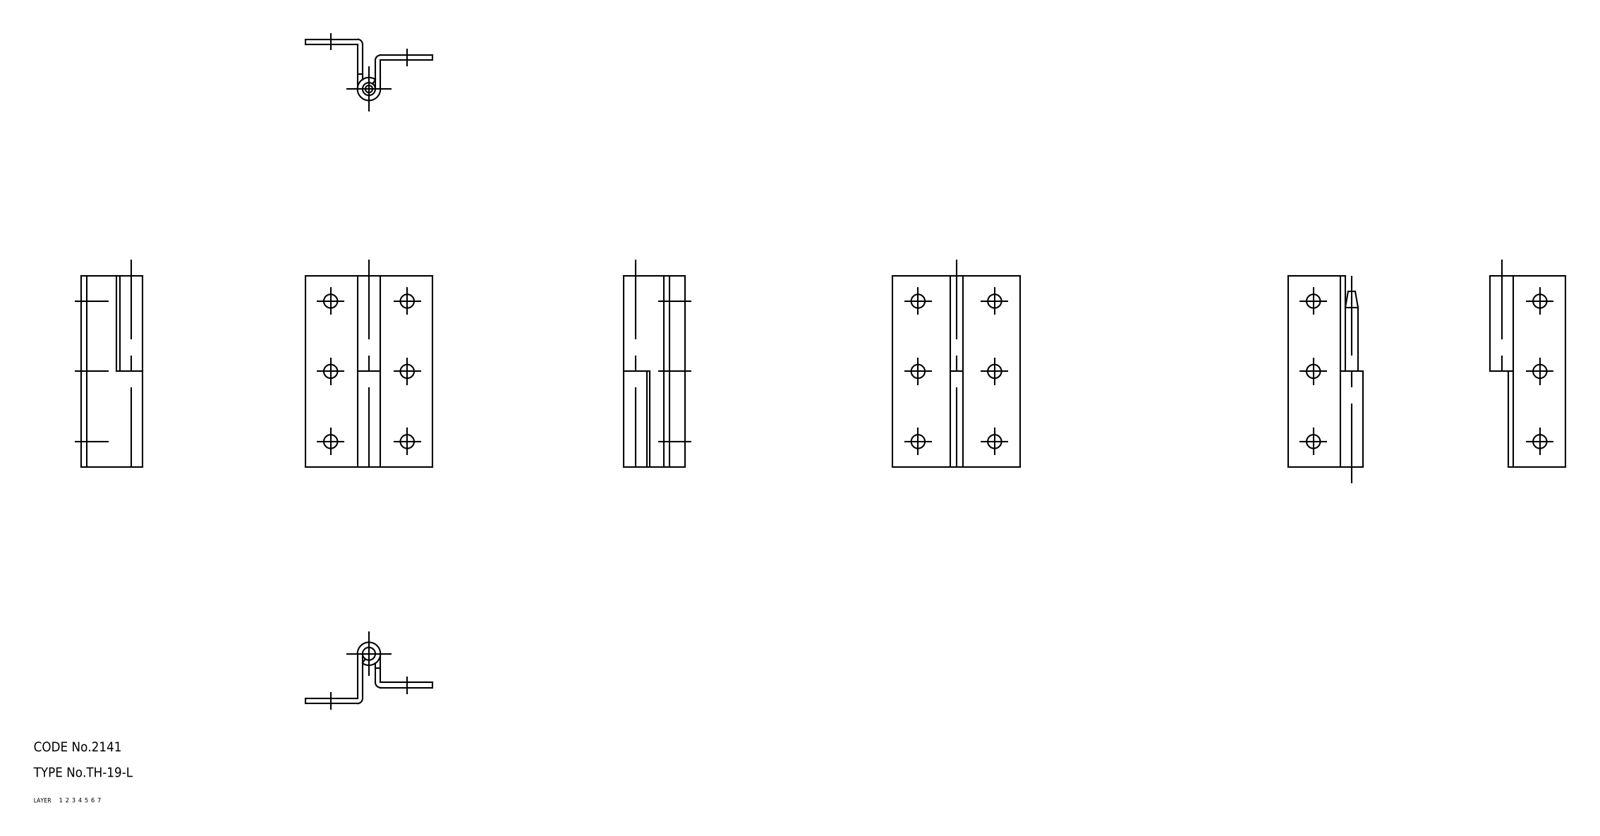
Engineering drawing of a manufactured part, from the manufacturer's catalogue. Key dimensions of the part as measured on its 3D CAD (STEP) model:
Part name (STEP PRODUCT): shaft; hinge piece_B; hinge piece_A; TH_19_L_5989_36
STEP written by: CADfix (AUTOMOTIVE_DESIGN)
Units: millimetres
Bodies: 3 solids, 44 faces (0 planar, 0 cylindrical, 44 other)
Overall size (bounding box): 60 × 40 × 19.2
Volume: 7 107 mm³ · Surface area: 9 537 mm²
